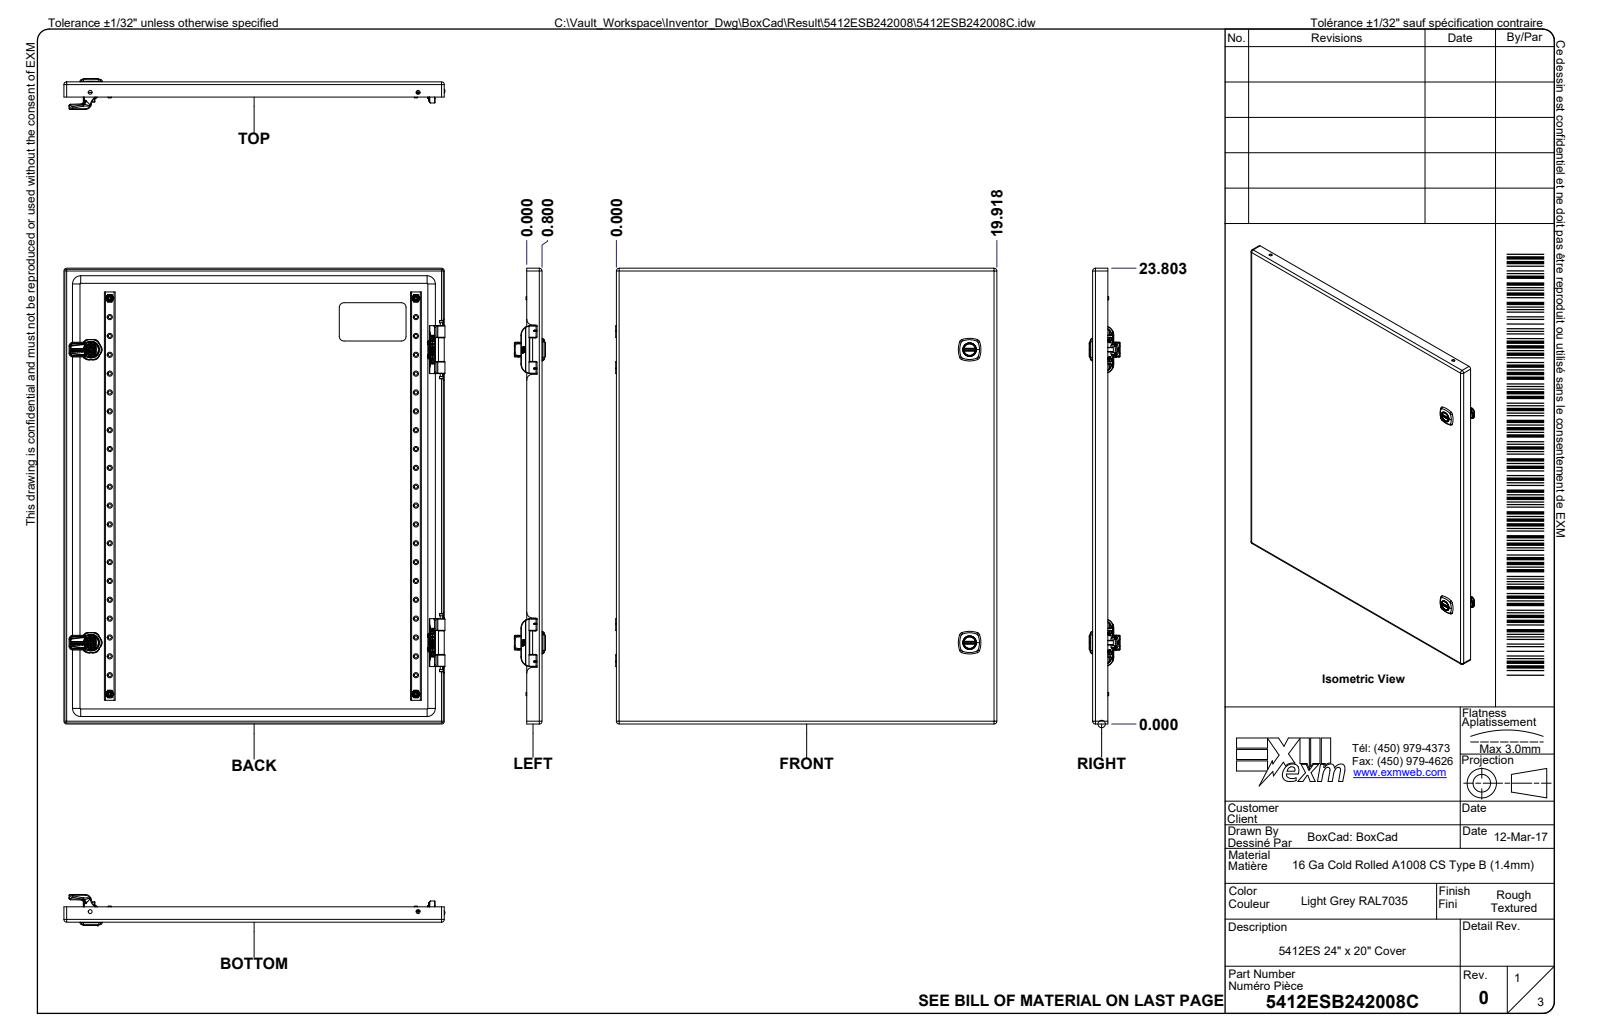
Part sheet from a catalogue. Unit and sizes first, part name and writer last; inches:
Units: inches
Overall size (bounding box): 24 × 20.003 × 9.31
Round holes (diameter × count): ⌀0.165 ×40, ⌀0.03 ×9, ⌀0.043 ×8, ⌀0.201 ×8, ⌀0.315 ×8, ⌀0.311 ×6, ⌀0.178 ×4, ⌀0.197 ×4, ⌀0.268 ×4, ⌀0.27 ×4, ⌀0.29 ×4, ⌀0.39 ×4
Round bosses / shafts (diameter × count): ⌀0.237 ×40, ⌀0.232 ×9, ⌀0.03 ×9, ⌀0.039 ×8, ⌀0.717 ×4, ⌀0.374 ×4, ⌀0.311 ×4, ⌀0.262 ×4
Partial cylindrical surfaces — rounded edges, fillets, slot ends (radius × count): R0.02 ×263, R0.01 ×139, R0.039 ×109, R0.008 ×94, R0.012 ×50, R0.031 ×32, R0.016 ×30, R0.084 ×24
Main face-to-face distances: 0.053, 9.081, 9.028, 9.135, 0.927, 0.874, 8.154, 8.207, 1.032, 0.979
Hole centre spacings: 1.969, 0.984, 2.953, 3.937, 15.303, 4.921, 5.906, 6.89
Volume: 156.9 in³ · Surface area: 4 948 in²
Bodies: 64 solids, 10070 faces (3049 planar, 2555 cylindrical, 4466 other)
Part name (STEP PRODUCT): 5412ESB242008; 5412ESB242008B; 5412ESB242008B-P; STK-Q-16005 (+8 more)
STEP written by: Autodesk Inventor 2024 (AUTOMOTIVE_DESIGN)
